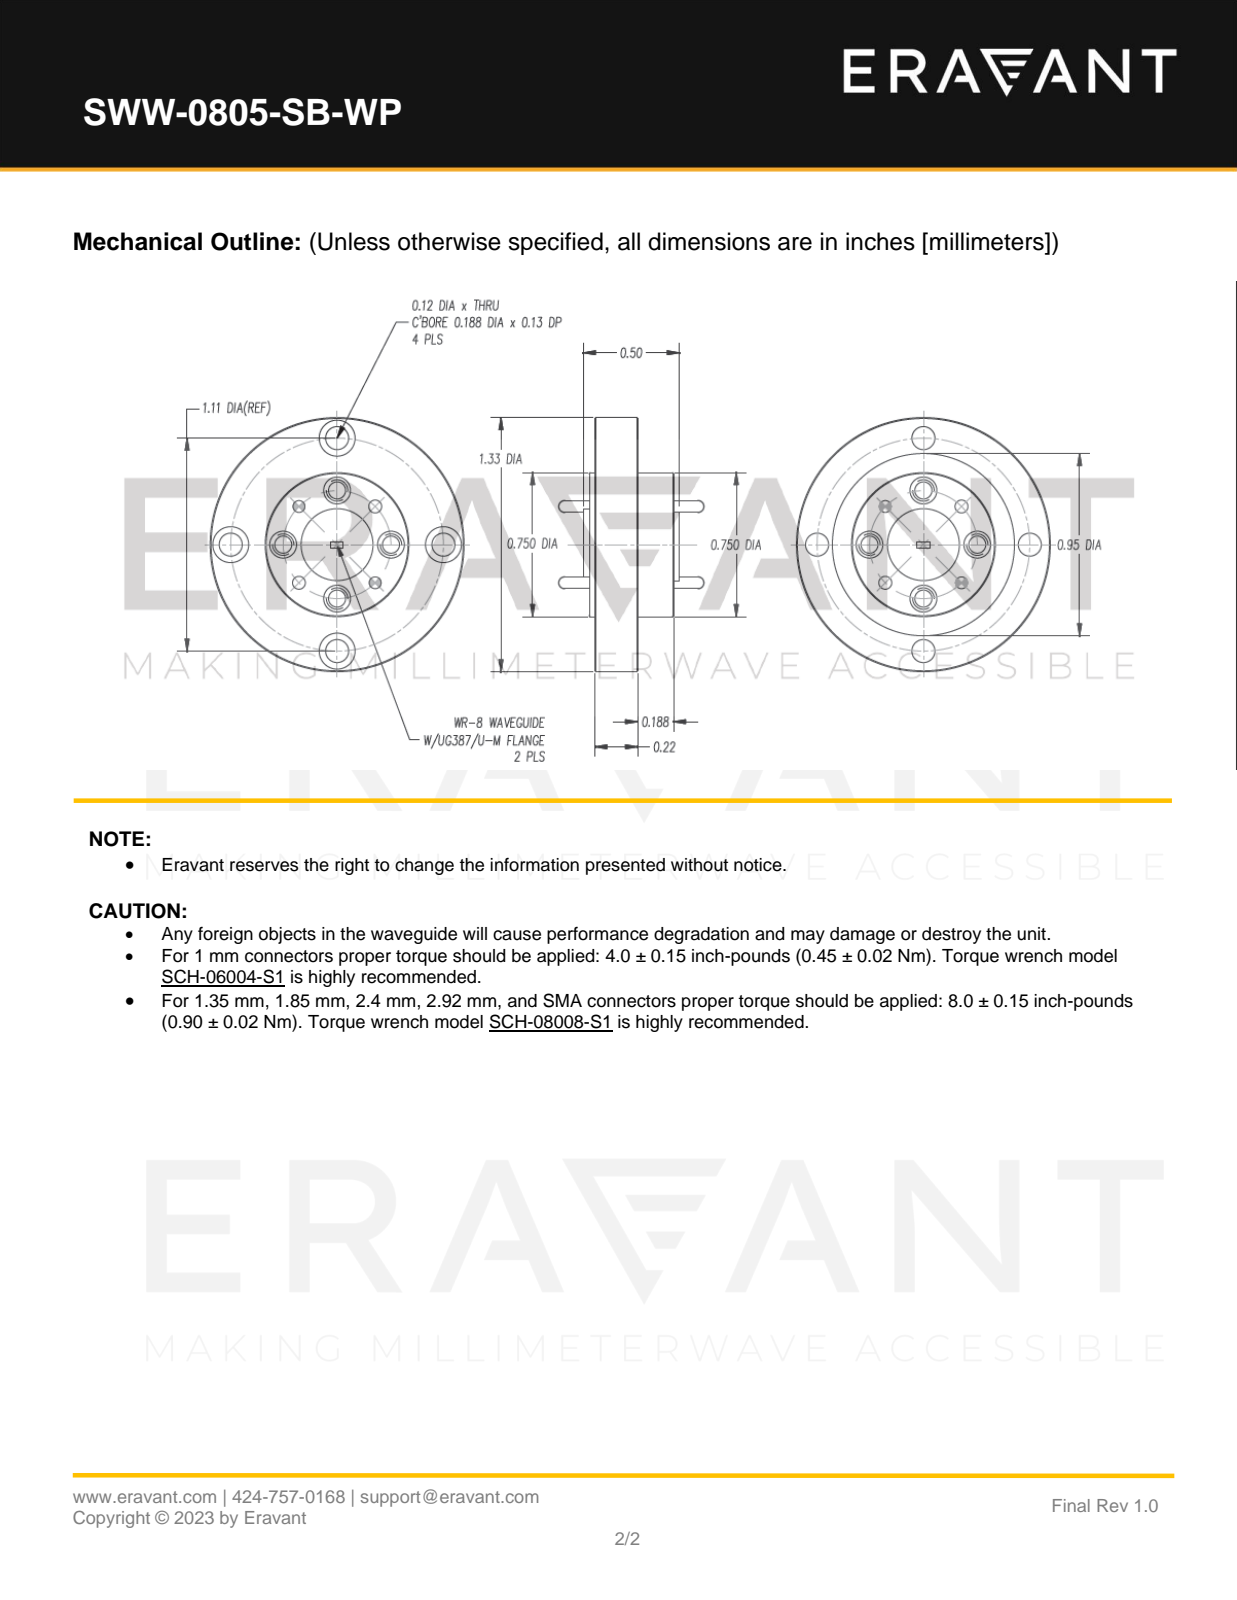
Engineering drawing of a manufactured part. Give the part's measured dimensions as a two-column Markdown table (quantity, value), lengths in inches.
| quantity | value |
| --- | --- |
| part name | DMWW-08-105-B |
| STEP written by | SolidWorks 2013 (CONFIG_CONTROL_DESIGN) |
| units | inches |
| bodies | 5 solids, 171 faces (47 planar, 84 cylindrical, 40 other) |
| overall size | 1.325 × 1.325 × 0.725 |
| volume | 0.357 in³ |
| surface area | 6.103 in² |
| round holes (diameter × count) | 0.061 × 4, 0.067 × 4, 0.089 × 4, 0.12 × 4, 0.14 × 4, 0.187 × 4, 0.95 × 1 |
| round bosses / shafts (diameter × count) | 0.063 × 4, 1.325 × 1, 0.75 × 1, 0.375 × 1 |
| main face-to-face distances | 0.222, 0.03, 0.44, 0.147, 0.075, 0.177, 0.252, 0.41, 0.263, 0.188 |
| hole center spacings | 0.215, 0.78, 0.52, 0.622, 0.398, 0.407, 0.274, 0.281 |
